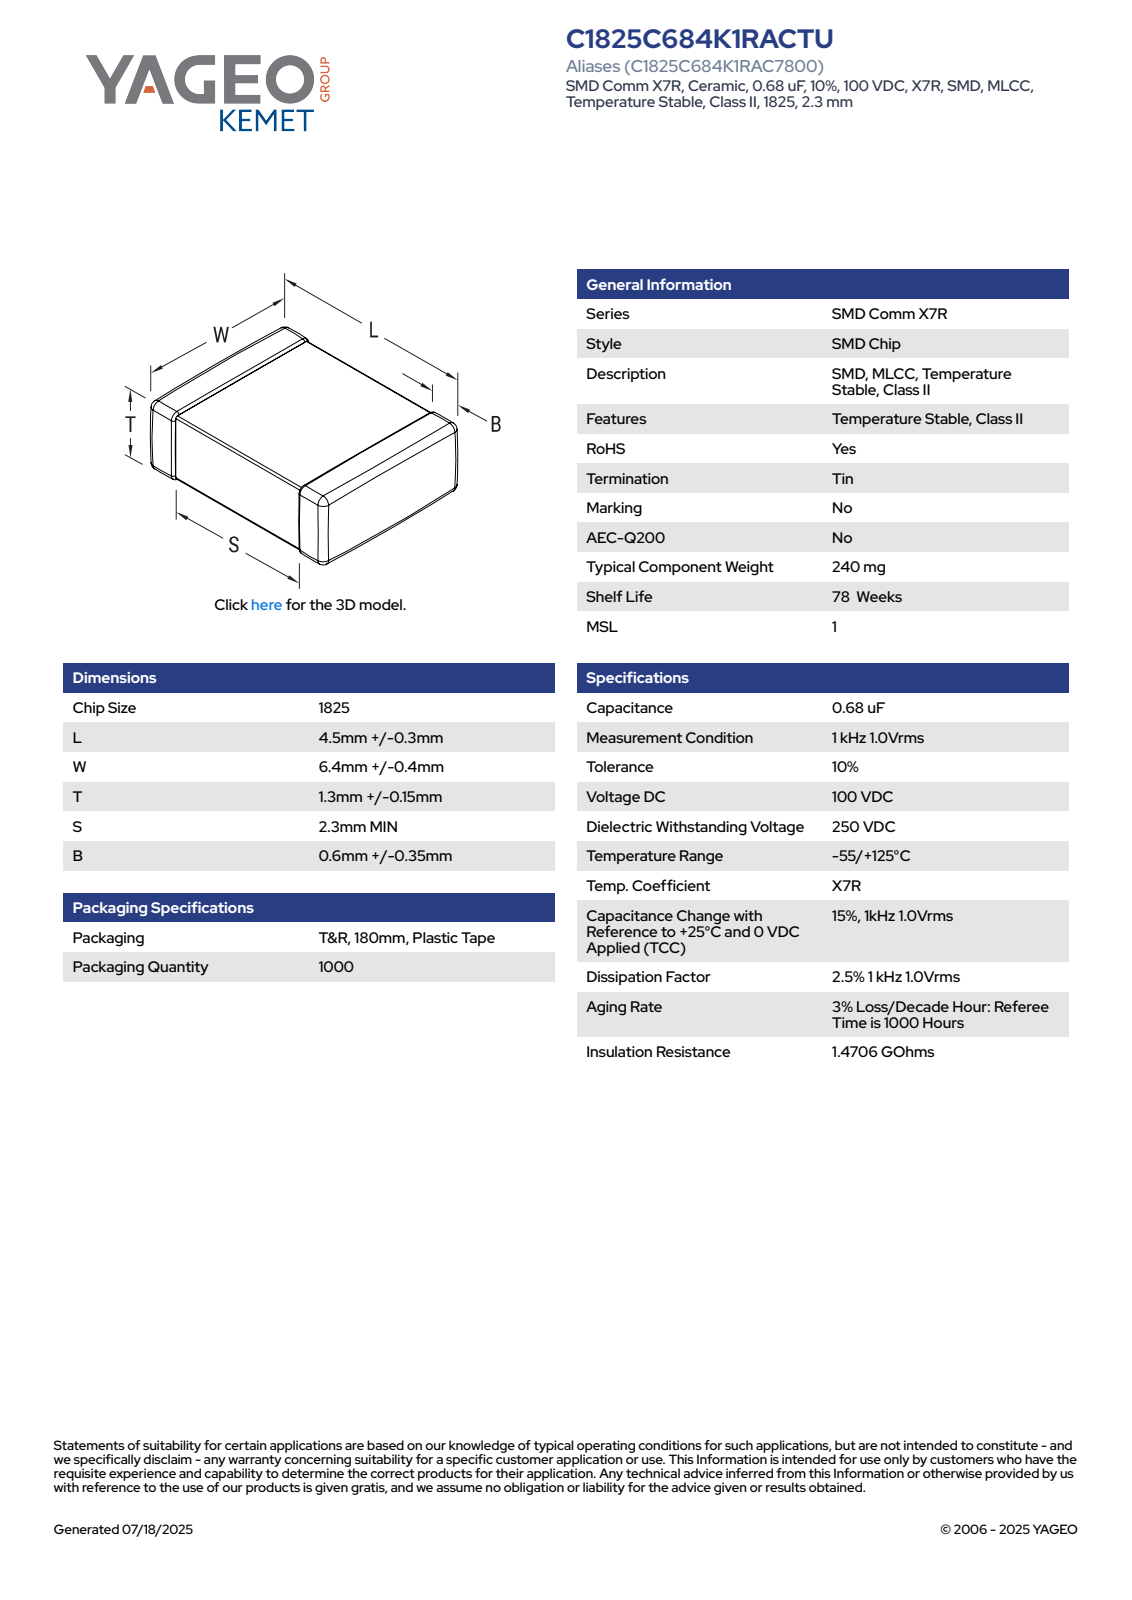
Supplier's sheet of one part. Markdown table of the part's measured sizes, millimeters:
| quantity | value |
| --- | --- |
| part name | CCS_CCSTDNOS_1825_L4.8W6.8T1.45B0.95 |
| STEP written by | SolidWorks 2014 (AUTOMOTIVE_DESIGN) |
| units | millimeters |
| bodies | 4 solids, 125 faces (71 planar, 38 cylindrical, 16 other) |
| overall size | 6.8 × 4.8 × 1.45 |
| volume | 40 mm³ |
| surface area | 96 mm² |
| partial cylindrical surfaces (radius × count) | 0.14 × 24 |
| main face-to-face distances | 1.17, 1.31, 1.45, 4.8, 6.66, 6.52, 6.8, 0.34, 3.56, 3.42 |
